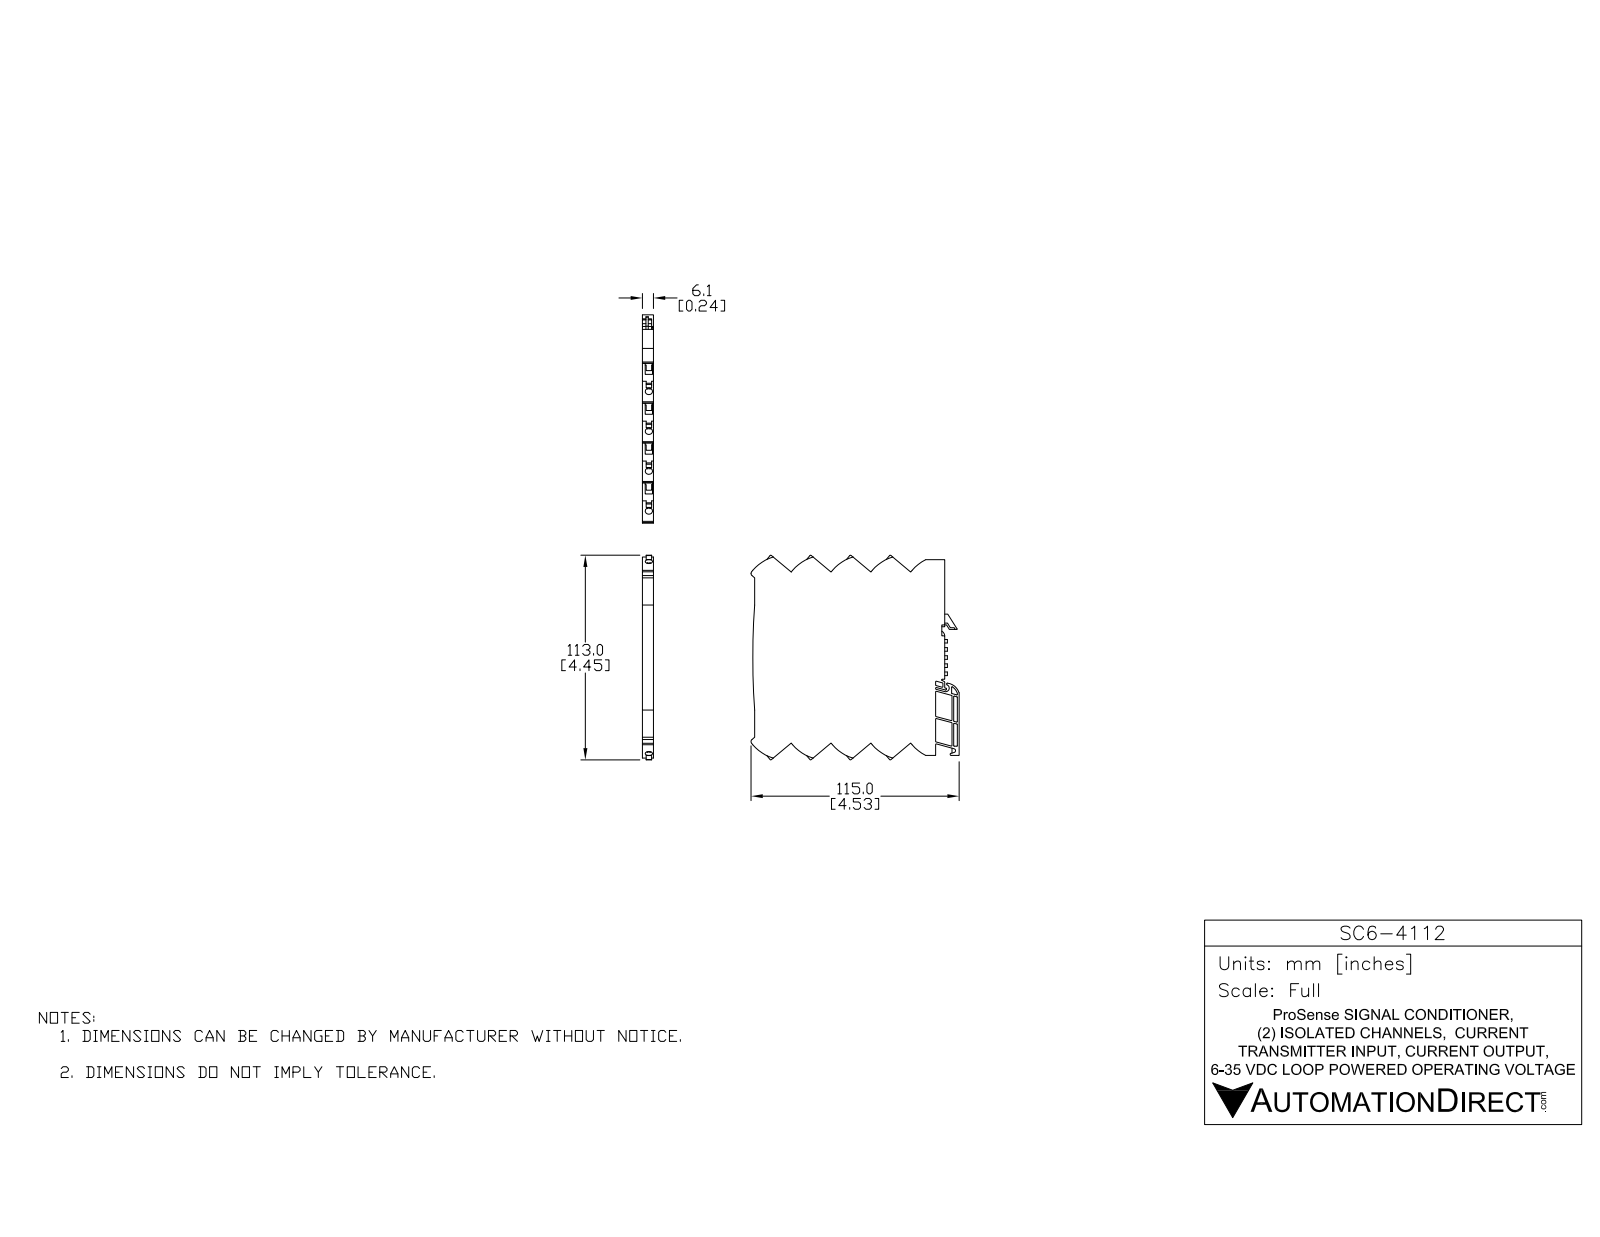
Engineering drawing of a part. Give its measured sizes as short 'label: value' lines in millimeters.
name: SC6-4112
written by: SolidWorks 2017 (AUTOMOTIVE_DESIGN)
unit: mm
bodies: 1 solid, 435 faces (328 planar, 107 cylindrical, 0 other)
size: 115 × 112.99 × 6.1
volume: 65 156 mm³; area: 28 033 mm²
holes: 8× ⌀4
rounds: 33× R0.3, 10× R0.5, 10× R1.5, 10× R23.31, 2× R0.2, 1× R0.57, 1× R1.08, 1× R2
face distances: 6.1, 1, 3, 4, 2.05, 14.14, 4.05, 1.05, 3.5, 5.05
hole spacings: 14.14, 28.28, 14.15, 42.42
